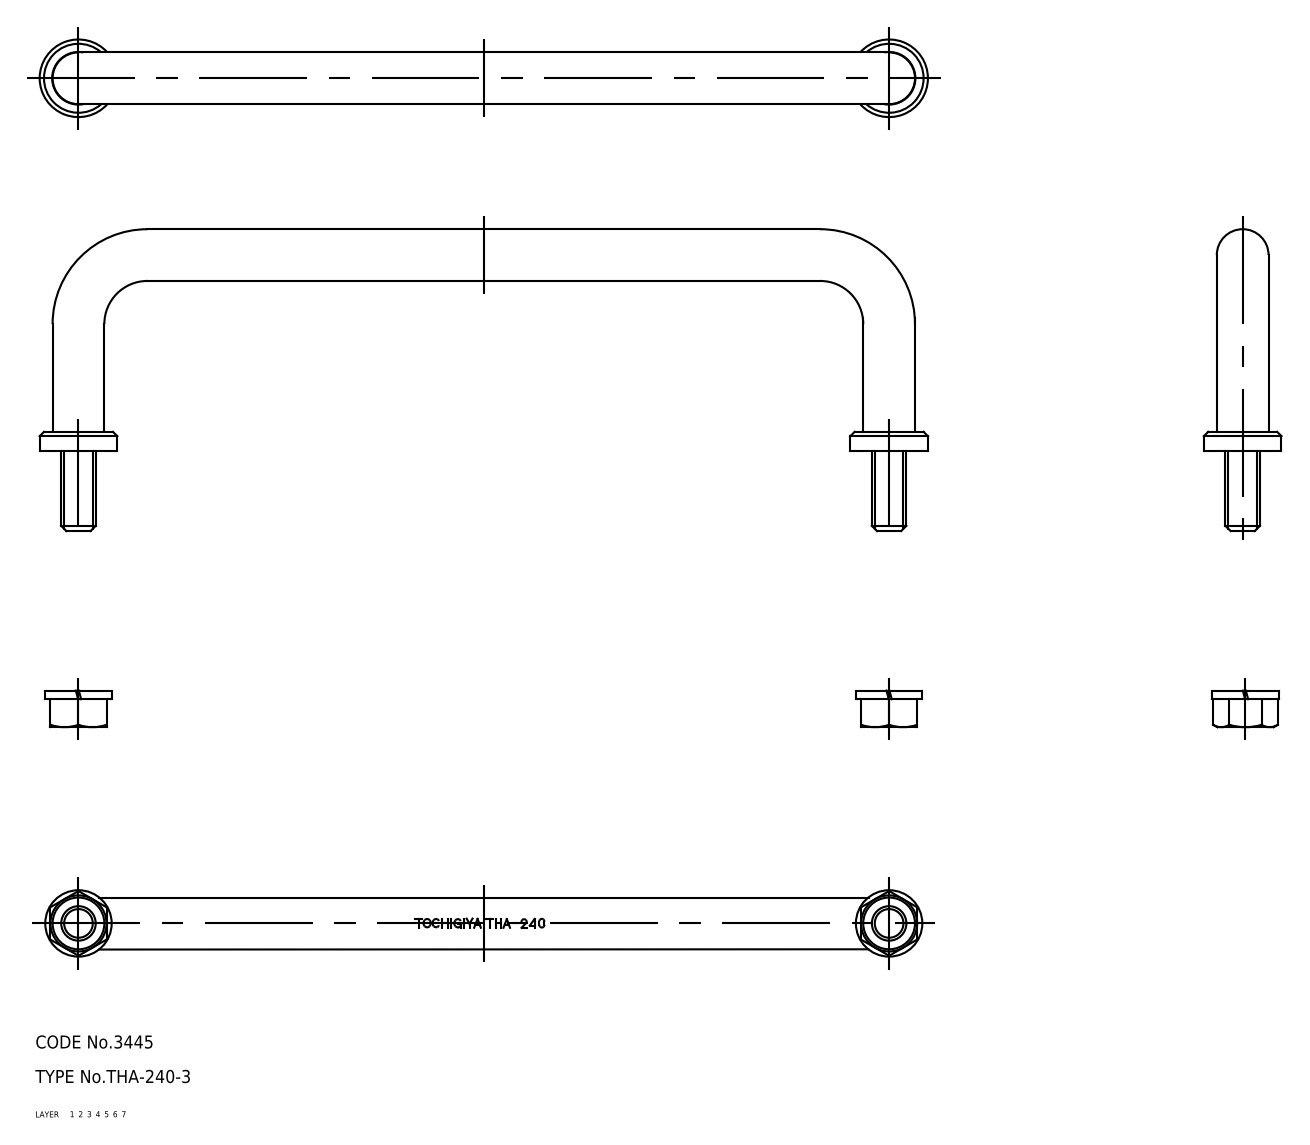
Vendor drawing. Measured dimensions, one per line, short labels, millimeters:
name: facing ring; nut; washer; pull (+1 more)
written by: CADfix (AUTOMOTIVE_DESIGN)
unit: mm
bodies: 7 solids, 86 faces (0 planar, 0 cylindrical, 86 other)
size: 206 × 70 × 18
volume: 34 843 mm³; area: 14 750 mm²
